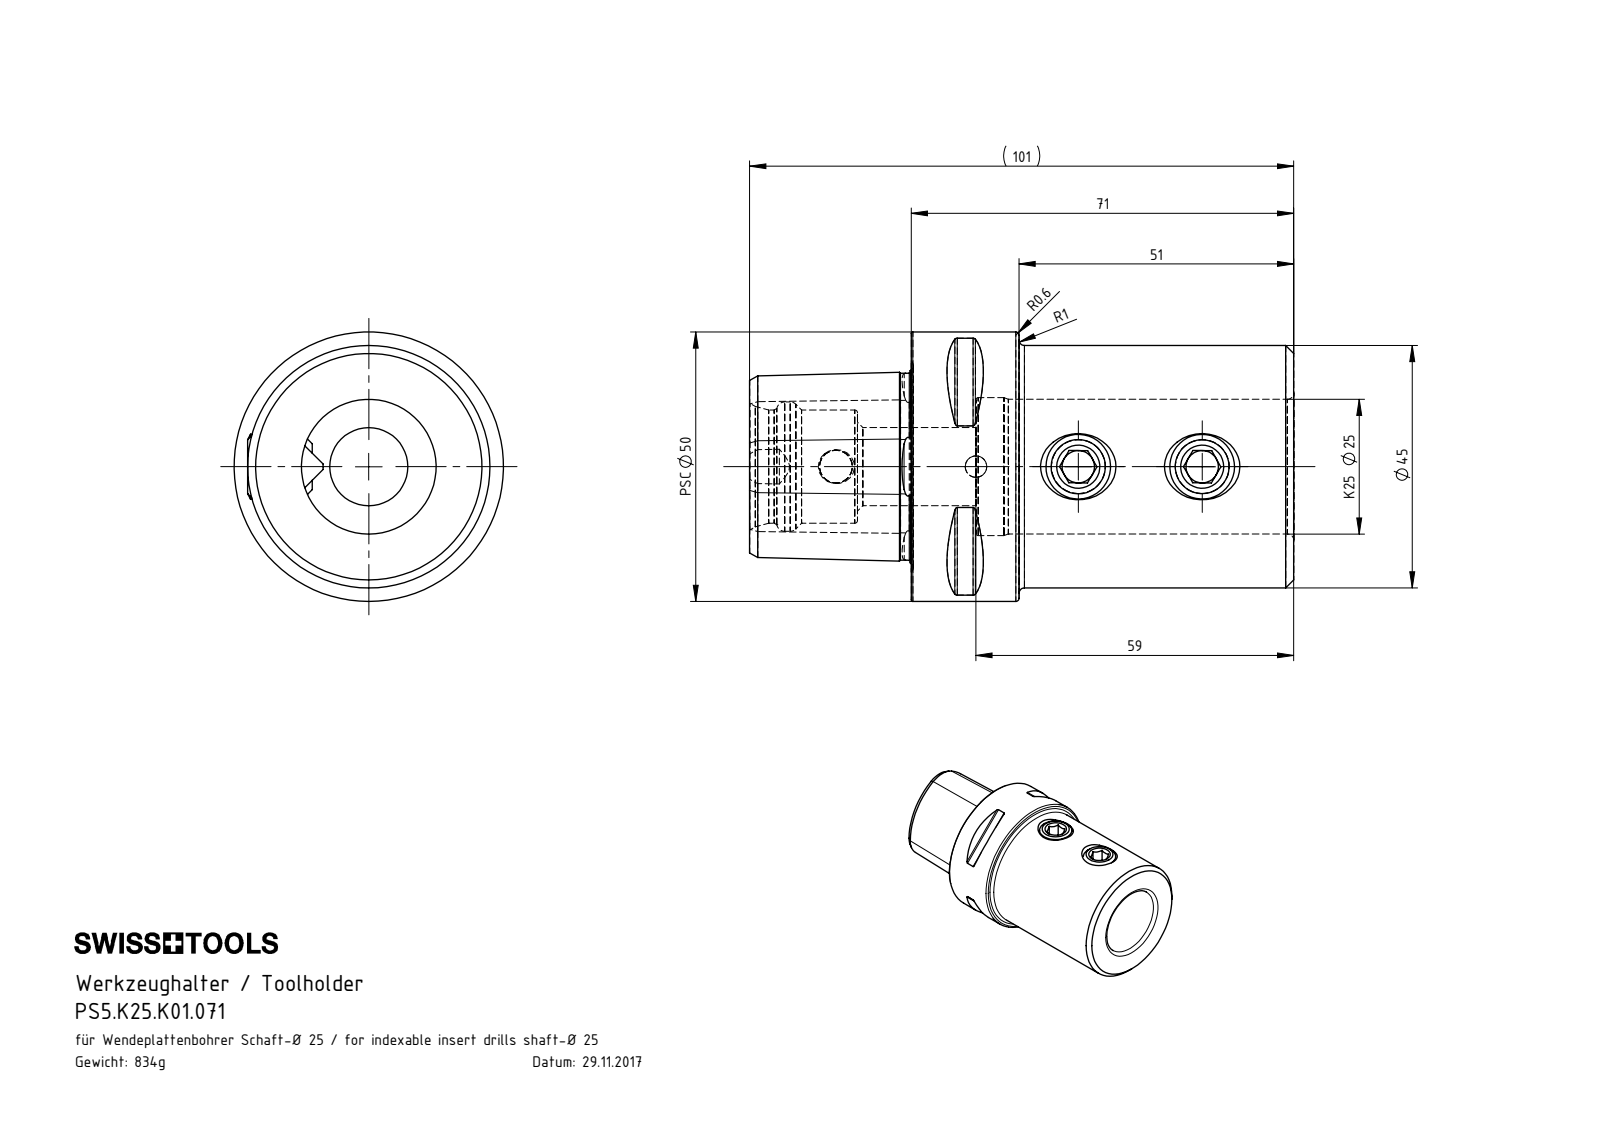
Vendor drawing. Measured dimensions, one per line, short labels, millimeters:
name: PS5-K25.K01.071_A; K32-ER2.012.014; PS5.K25.K01.071; K32-ER1.012.012_M12x12
written by: SolidWorks 2017 (AUTOMOTIVE_DESIGN)
unit: mm
bodies: 3 solids, 139 faces (49 planar, 26 cylindrical, 64 other)
size: 101 × 50 × 50
volume: 105 980 mm³; area: 25 948 mm²
holes: 2× ⌀6, 2× ⌀11, 1× ⌀4, 1× ⌀6.1, 1× ⌀14.5, 1× ⌀21, 1× ⌀24, 1× ⌀25, 1× ⌀25.6
bosses: 2× ⌀12, 1× ⌀50, 1× ⌀45
rounds: 8× R0.5, 1× R4
face distances: 71, 30, 12, 101, 42, 59, 20, 19.18, 8, 50
hole spacings: 19, 23, 26, 42, 45, 68
